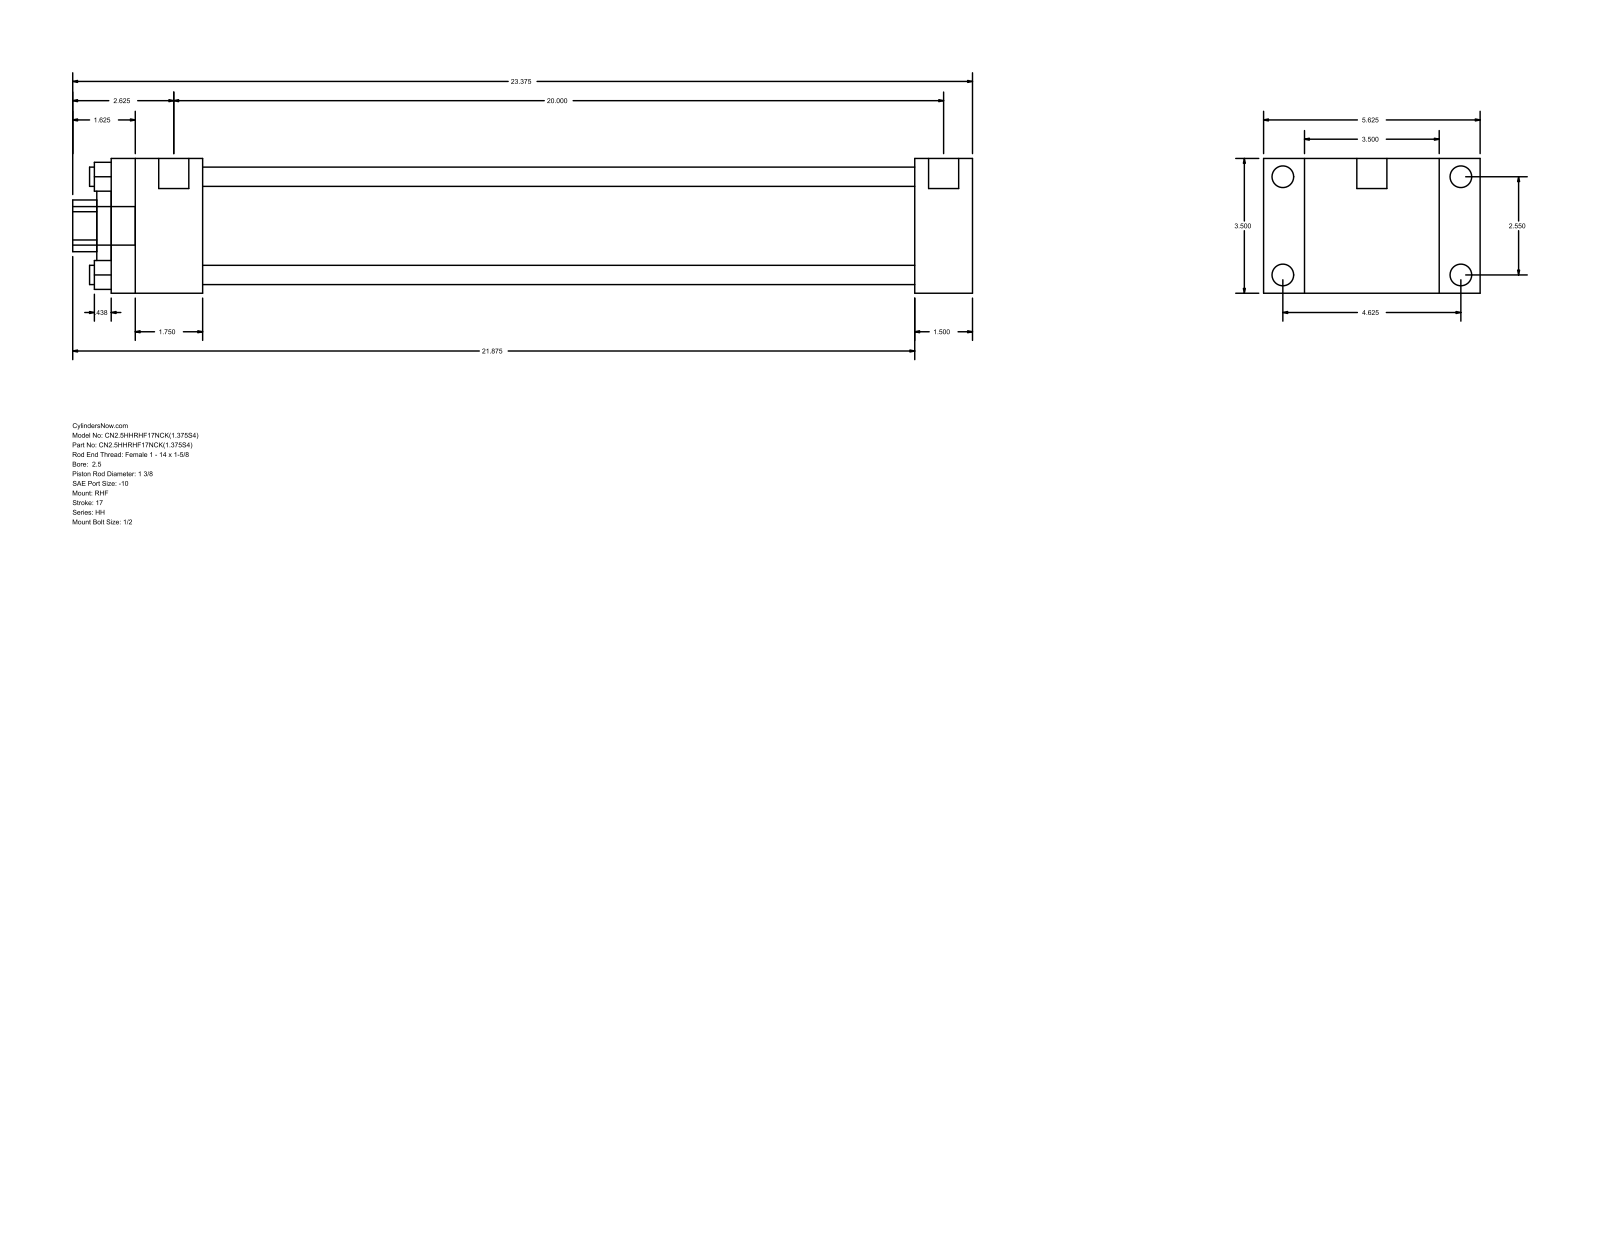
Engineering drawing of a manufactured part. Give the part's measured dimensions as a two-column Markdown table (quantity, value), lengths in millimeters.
| quantity | value |
| --- | --- |
| part name | HH_RHF__0250_1.375 |
| STEP written by | GSSL Pune (CONFIG_CONTROL_DESIGN) |
| units | millimeters |
| bodies | 0 solids, 88 faces (60 planar, 28 cylindrical, 0 other) |
| overall size | 593.73 × 142.88 × 88.9 |
| round holes (diameter × count) | 12.7 × 4, 34.92 × 1, 50.8 × 1, 73.03 × 1 |
| round bosses / shafts (diameter × count) | 14.3 × 4, 5.56 × 4, 19.84 × 2, 25.4 × 1 |
| partial cylindrical surfaces (radius × count) | 17.06 × 1 |
| main face-to-face distances | 88.9, 38.11, 26.99, 115.89, 530.22, 568.33, 142.88, 60.32, 469.9, 508.01 |
| hole center spacings | 45.79, 64.76, 91.58 |
